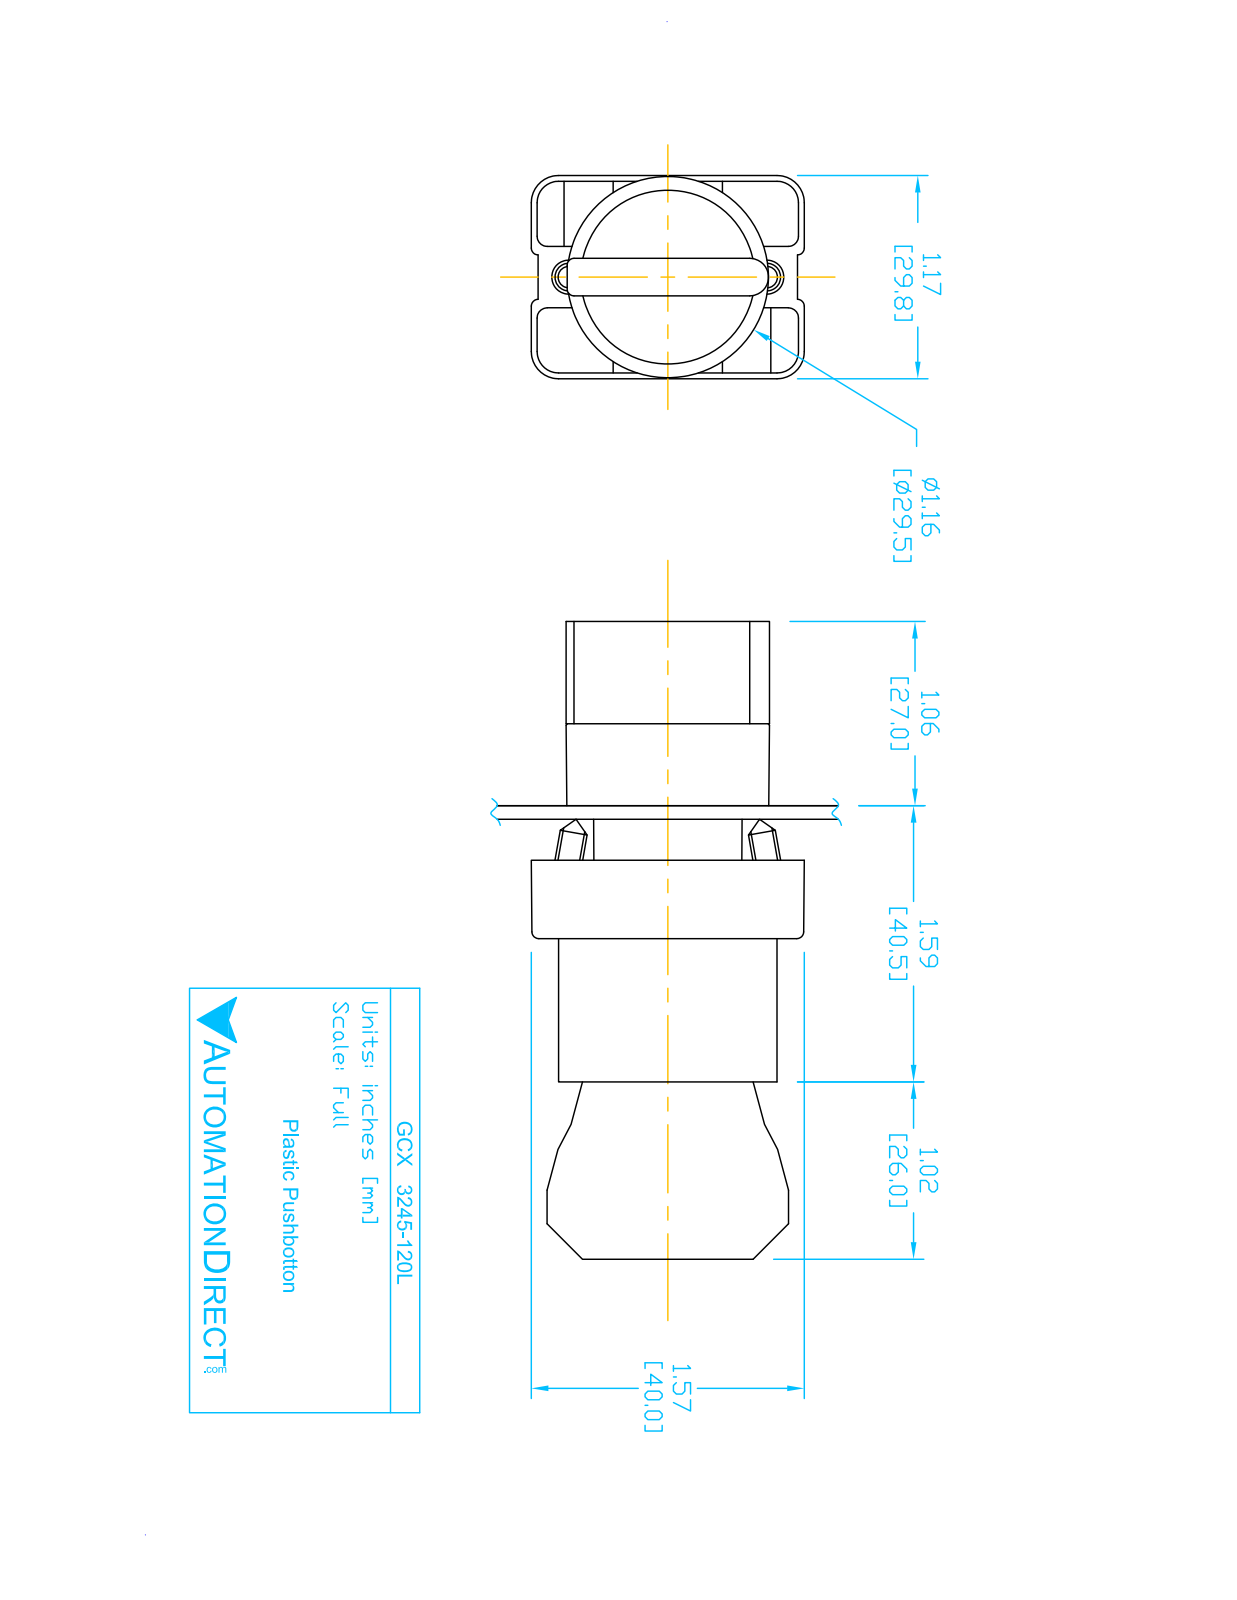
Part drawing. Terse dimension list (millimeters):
name: GCX3245-120L; ecx1040; GCX3245L OPERATOR; ECX3029-2 (+1 more)
written by: SolidWorks 2016 (AUTOMOTIVE_DESIGN)
unit: mm
bodies: 8 solids, 445 faces (263 planar, 151 cylindrical, 31 other)
size: 92.8 × 40.2 × 29.9
volume: 45 870 mm³; area: 25 160 mm²
holes: 2× ⌀2, 2× ⌀3.1, 2× ⌀3.3, 1× ⌀2.2, 1× ⌀5, 1× ⌀11.9, 1× ⌀22.3, 1× ⌀22.6, 1× ⌀26
bosses: 4× ⌀4, 1× ⌀29.8, 1× ⌀25.5, 1× ⌀24, 1× ⌀21.7, 1× ⌀19.8, 1× ⌀12.8
rounds: 24× R1.5, 12× R1, 12× R3.1, 12× R4, 9× R1, 2× R3.3, 1× R0.5, 1× R1.6
face distances: 21, 51.3, 30.3, 14.7, 31.6, 29.7, 12, 11.9, 0.8, 0.8
hole spacings: 6, 13.8, 12, 12.4
